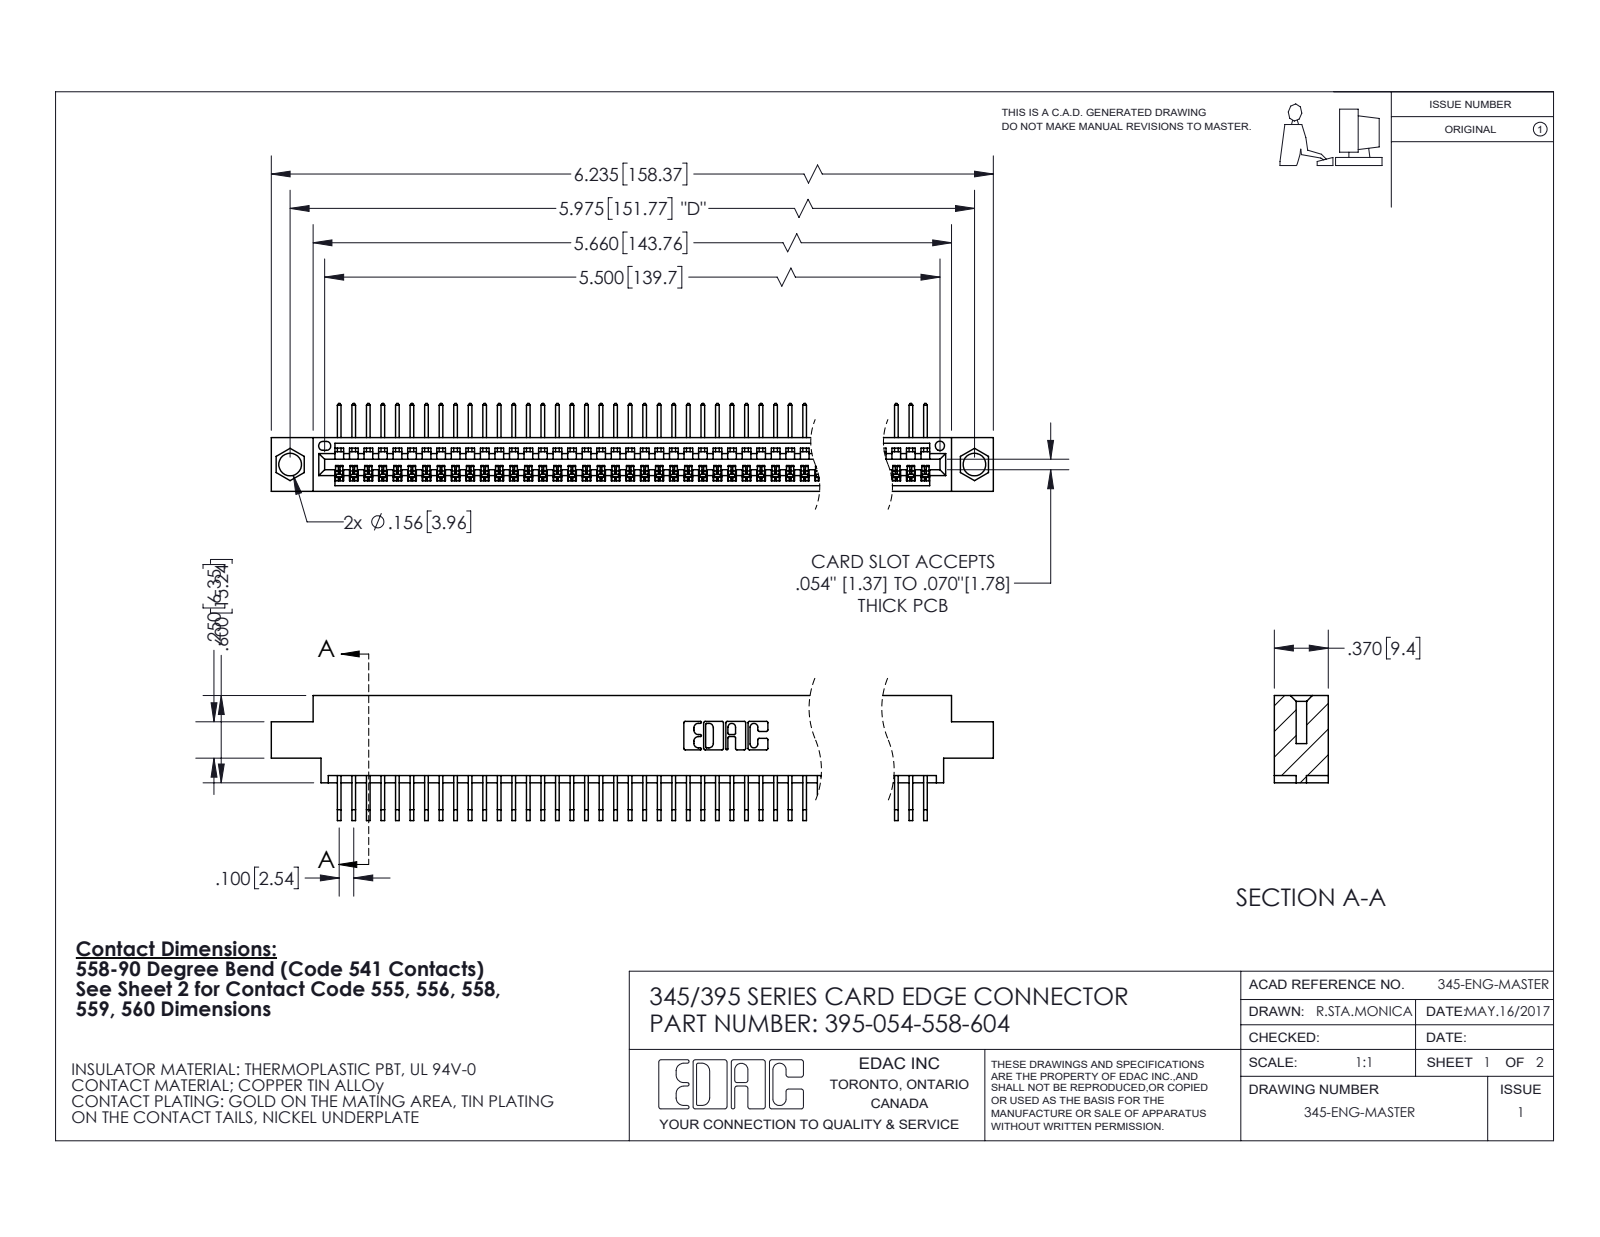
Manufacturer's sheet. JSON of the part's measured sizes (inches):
{"part_name": "395-054-558-604; 345-292-001_558 Tail - 2; 345 Part_0.170 Offset - 0.156 Dia-TI", "step_written_by": "SolidWorks 2020 (CONFIG_CONTROL_DESIGN)", "units": "inches", "bodies": {"solids": 55, "faces": 3384, "planar": 2366, "cylindrical": 1018, "other": 0}, "overall_size": [6.235, 0.859, 0.605], "volume_in3": 0.922, "surface_area_in2": 32.95, "round_holes": [[0.156, 2], [0.064, 1]], "partial_cylinders_radius": [[0.006, 108], [0.01, 22], [0.007, 6], [0.031, 6], [0.026, 3], [0.031, 2], [0.04, 2], [0.014, 1]], "face_to_face_distances": [0.072, 0.298, 0.37, 0.2, 0.098, 0.272, 0.025, 0.225, 0.175, 0.149], "hole_center_spacings": [0.27, 5.739, 5.975]}
